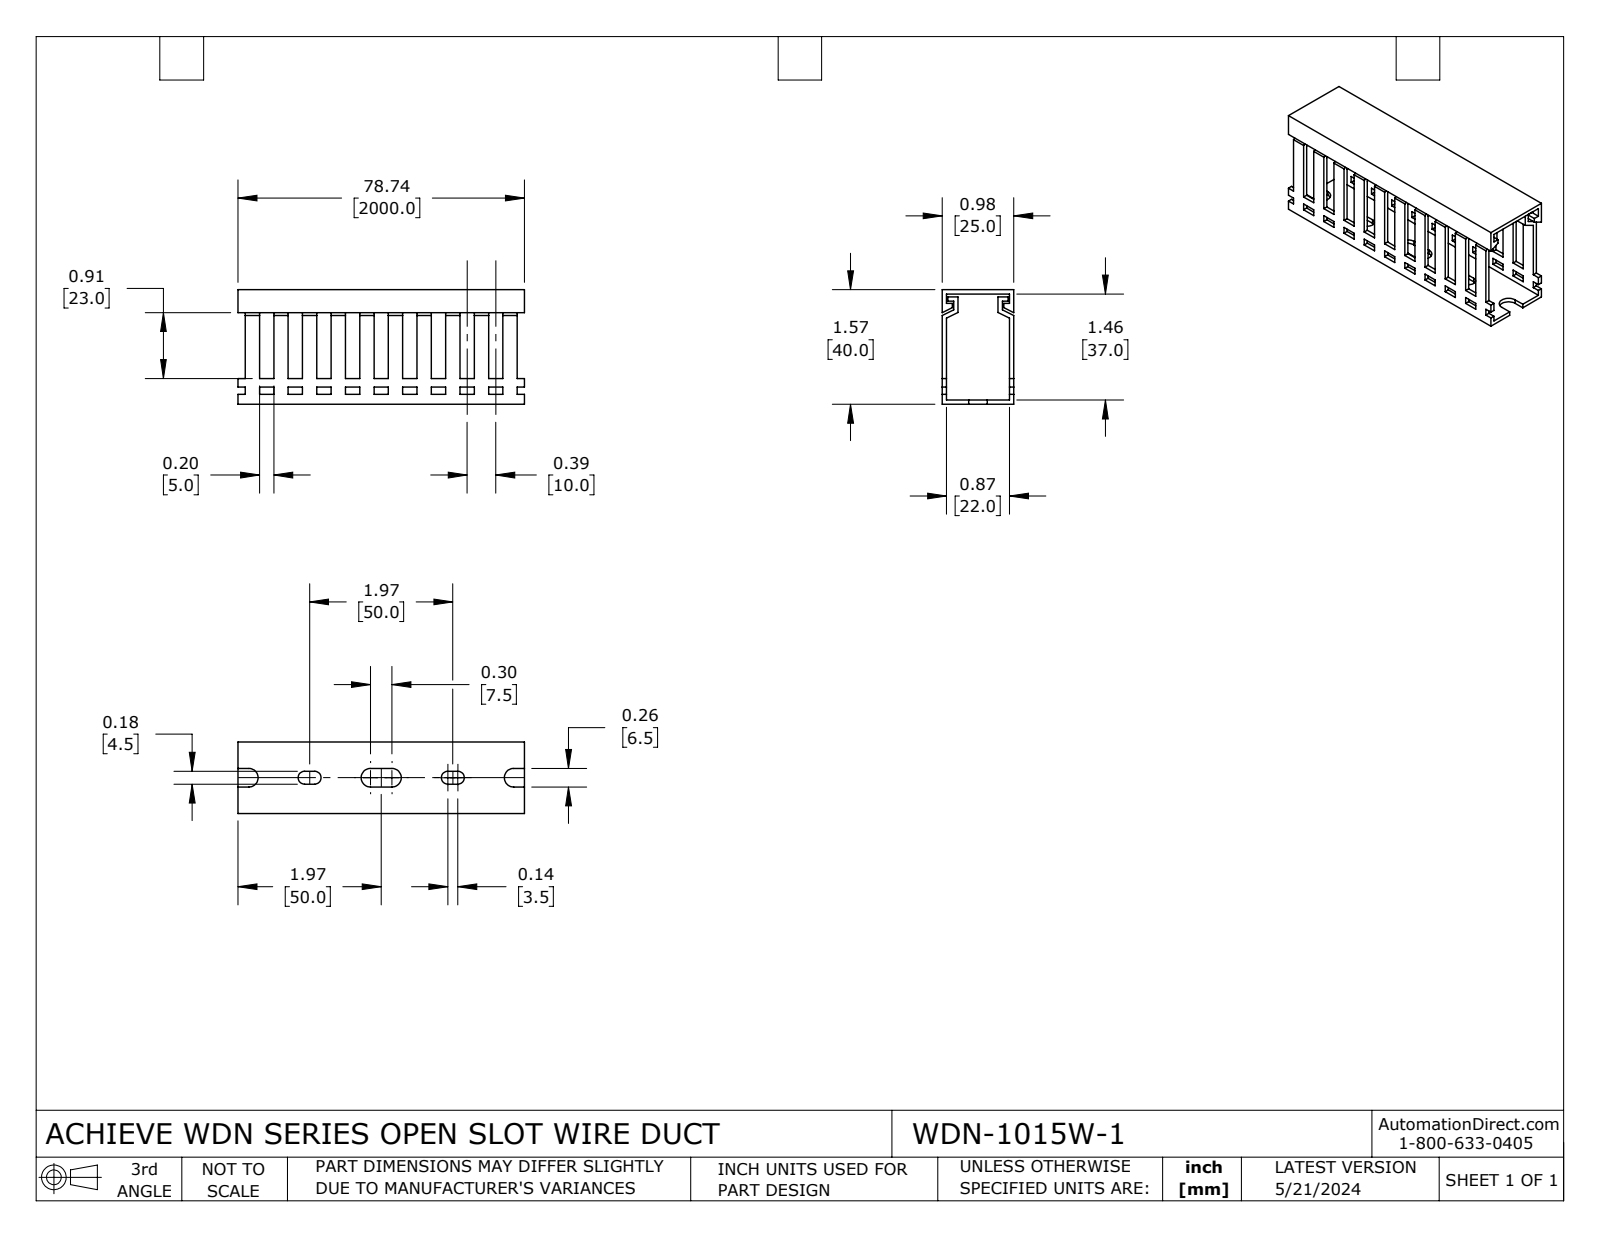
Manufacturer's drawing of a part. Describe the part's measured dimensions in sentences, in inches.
The part is named "WDN-1015W-1". Its 3-D file was written by "SolidWorks 2023 (CONFIG_CONTROL_DESIGN)". It is 2 solids with 336 faces: 324 planar, 12 cylindrical and 0 other. Overall it measures 3.937 by 1.575 by 0.984 inches. Its volume is 1.014 cubic inches and its surface area 39.04 square inches. Partial cylindrical surfaces (rounded edges, fillets, slot ends): 4 of radius 0.089, 4 of radius 0.128. The main face-to-face distances are 0.059, 1.516, 0.925, 0.984, 1.575, 0.866, 1.457, 0.197, 0.787, 0.394.
